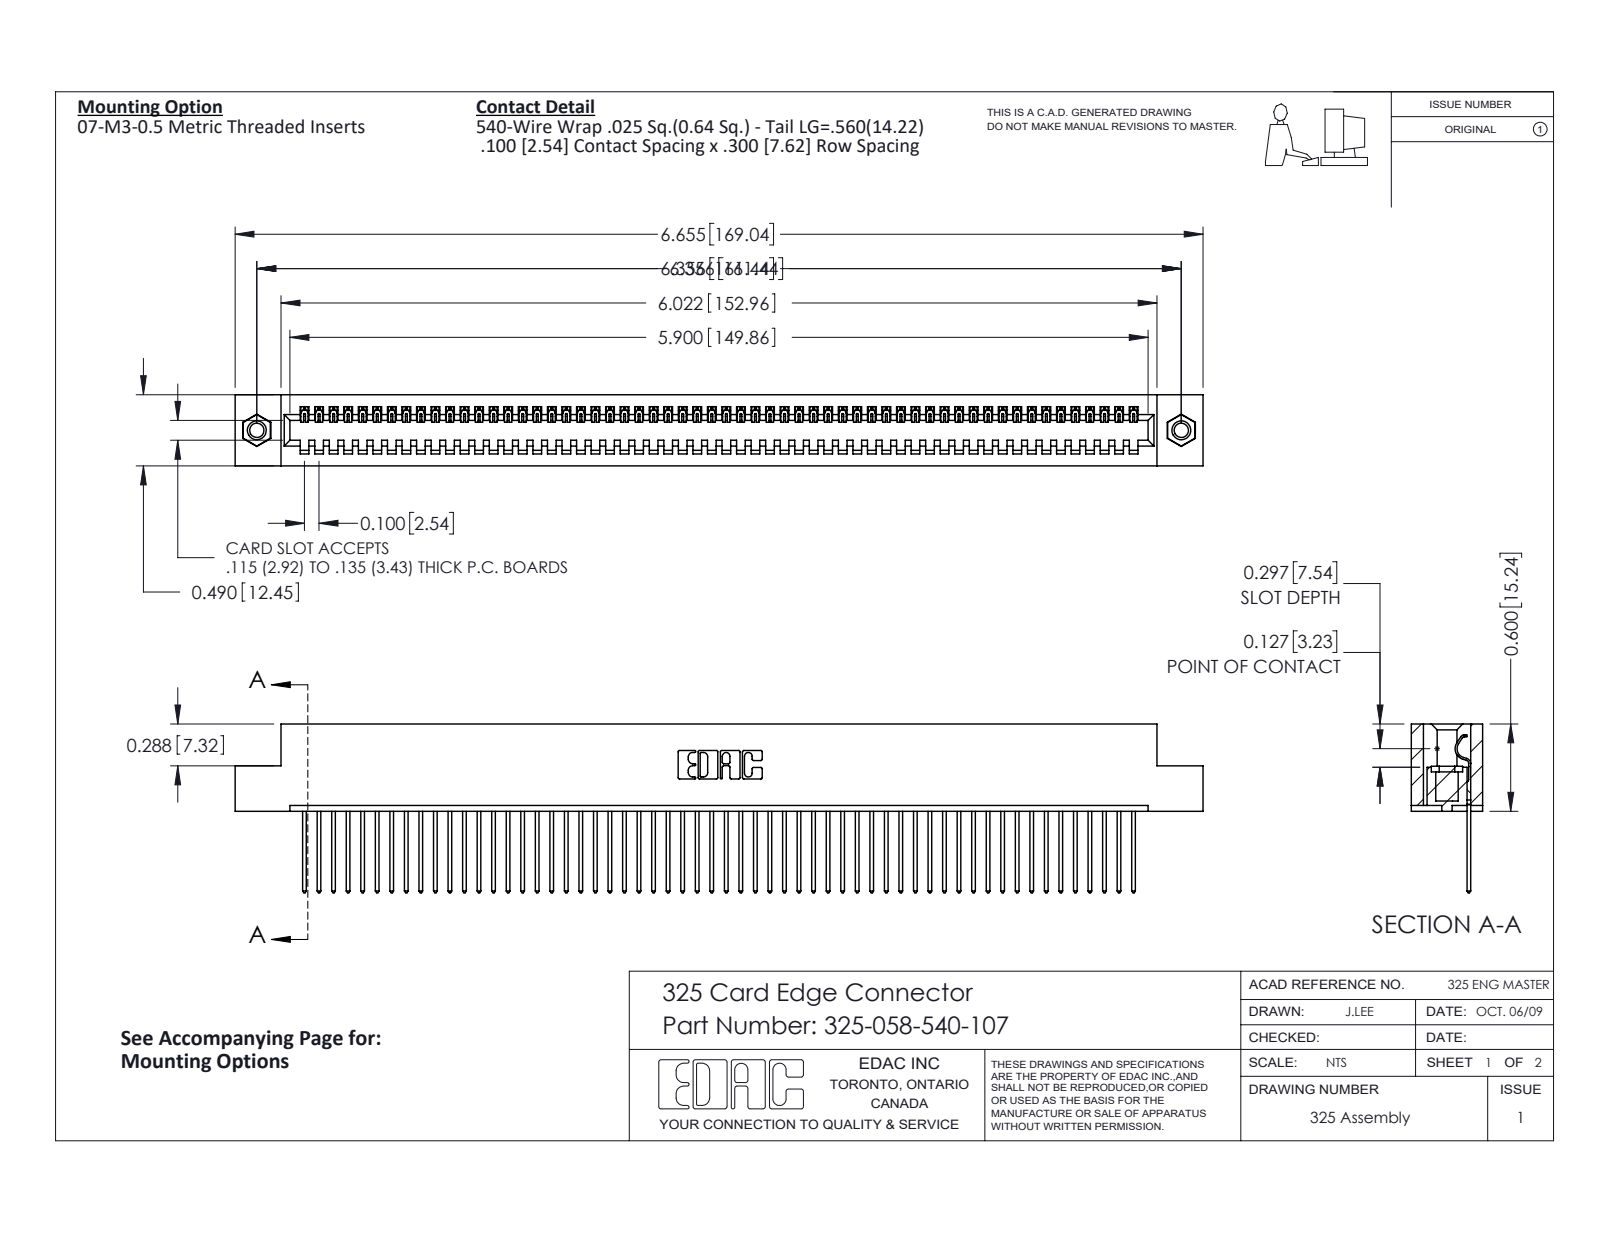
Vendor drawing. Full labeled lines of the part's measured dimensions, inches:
Part name (STEP PRODUCT): 325 Part_TI; 325-292-001_325-293-140; 345-250-001_345-250-005-103; 325-058-540-107
STEP written by: SolidWorks 2016 (CONFIG_CONTROL_DESIGN)
Units: inches
Bodies: 61 solids, 3538 faces (2538 planar, 984 cylindrical, 16 other)
Overall size (bounding box): 6.655 × 1.16 × 0.49
Volume: 1.321 in³ · Surface area: 38.03 in²
Round holes (diameter × count): ⌀0.098 ×2, ⌀0.125 ×2, ⌀0.16 ×2
Round bosses / shafts (diameter × count): ⌀0.155 ×2
Partial cylindrical surfaces — rounded edges, fillets, slot ends (radius × count): R0.006 ×116, R0.01 ×116, R0.01 ×22, R0.007 ×6, R0.031 ×6, R0.026 ×3, R0.014 ×1, R0.022 ×1
Main face-to-face distances: 0.083, 0.407, 0.49, 0.107, 0.383, 0.025, 0.3, 0.325, 0.263, 0.56
Hole centre spacings: 6.356
